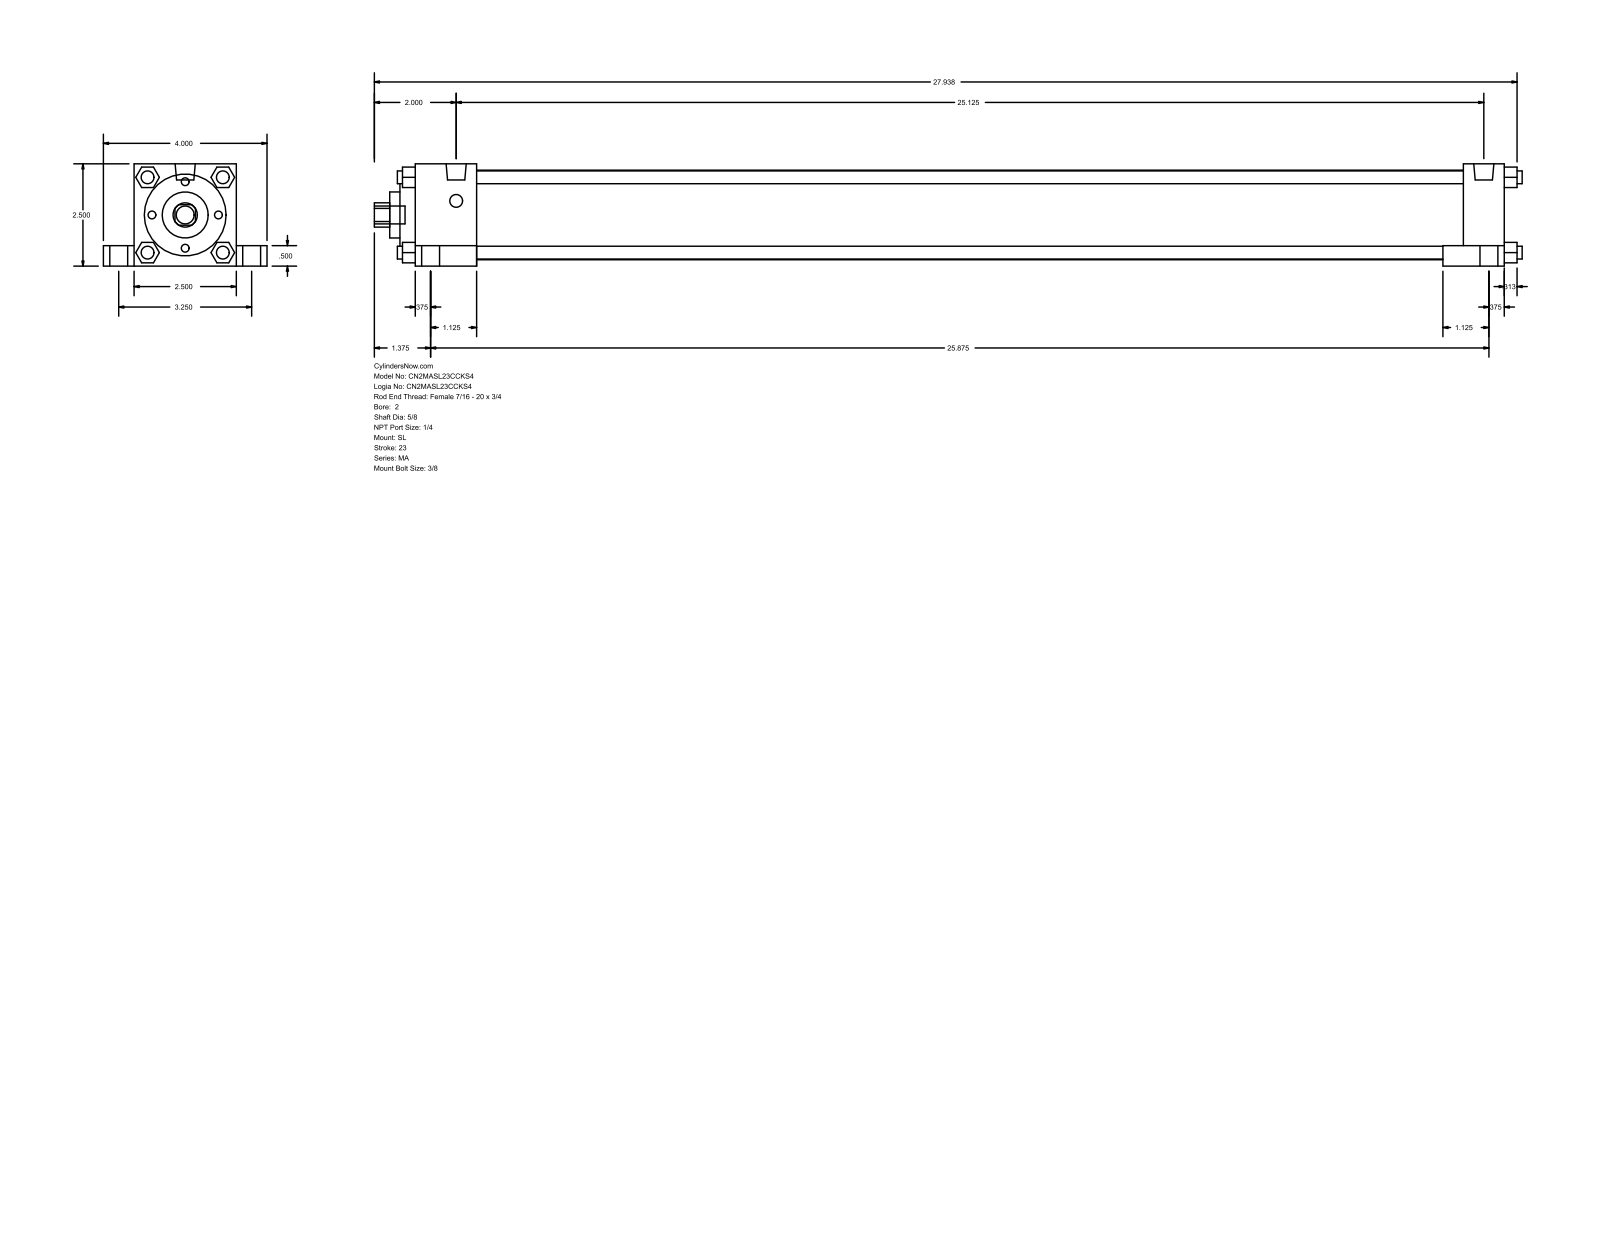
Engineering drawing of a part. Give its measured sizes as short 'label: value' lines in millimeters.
name: MA_SL__0200_0.625
written by: GSSL Pune (CONFIG_CONTROL_DESIGN)
unit: mm
bodies: 0 solids, 150 faces (113 planar, 37 cylindrical, 0 other)
size: 712.79 × 101.6 × 63.5
holes: 1× ⌀15.88, 1× ⌀28.57, 1× ⌀50.8, 1× ⌀55.63
bosses: 8× ⌀7.94, 5× ⌀11.11, 4× ⌀17.46, 2× ⌀12.49
rounds: 1× R7.54
face distances: 63.5, 12.7, 9.52, 612.77, 25.4, 19.05, 82.55, 38.1, 676.27, 50.8
